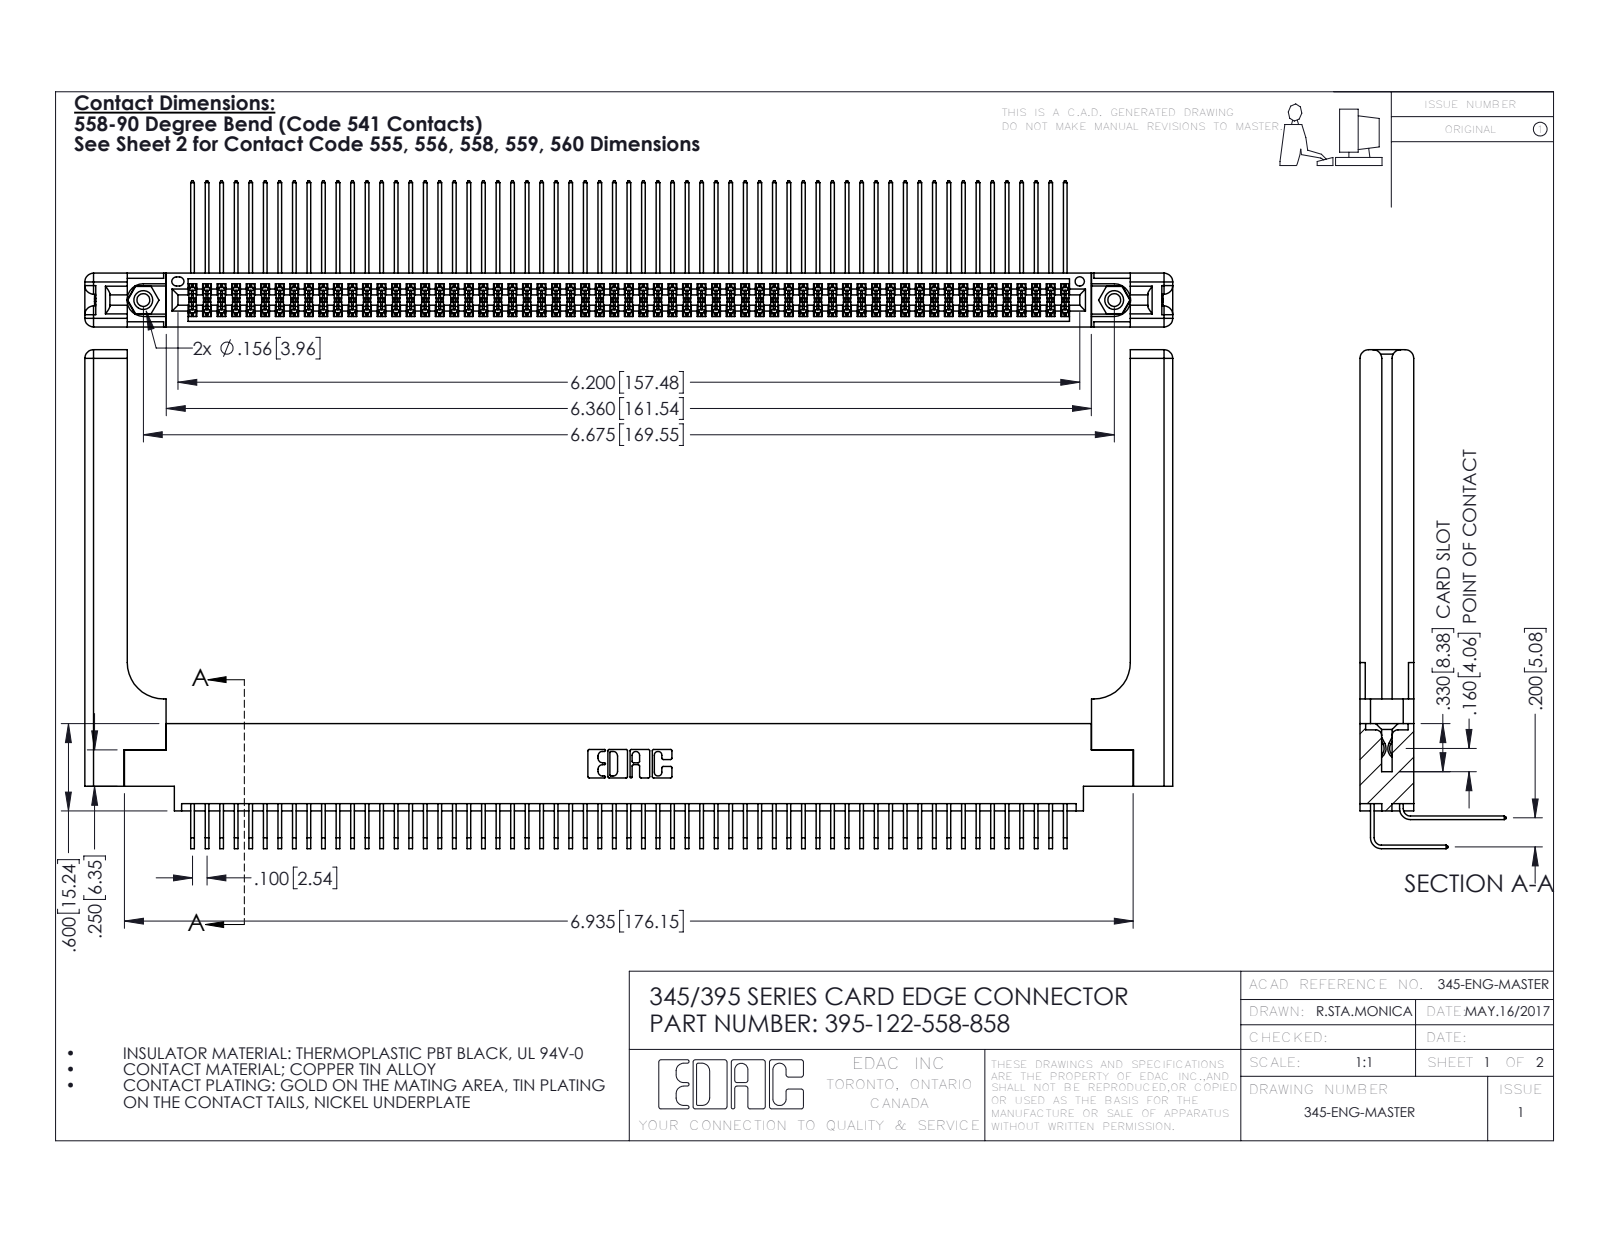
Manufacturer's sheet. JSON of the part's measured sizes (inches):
{"part_name": "345 Part_0.170 Offset - 0.156 Dia-TH; 345-250-001_345-250-001-102; 345-292-001_558 Tail - 2; 345-292-001_558 559 Tail - 1 (+2 more)", "step_written_by": "SolidWorks 2016 (CONFIG_CONTROL_DESIGN)", "units": "inches", "bodies": {"solids": 127, "faces": 6730, "planar": 4502, "cylindrical": 2168, "other": 60}, "overall_size": [7.479, 3.429, 1.005], "volume_in3": 1.69, "surface_area_in2": 57.8, "round_holes": [[0.089, 2], [0.125, 2], [0.156, 2], [0.064, 1]], "round_bosses_or_shafts": [[0.155, 2]], "partial_cylinders_radius": [[0.006, 183], [0.01, 22], [0.06, 16], [0.007, 6], [0.031, 6], [0.026, 3], [0.014, 2], [0.019, 2]], "face_to_face_distances": [0.072, 0.298, 0.37, 0.2, 0.098, 0.272, 0.025, 0.225, 0.175, 0.148], "hole_center_spacings": [0.27, 6.439, 6.675]}
